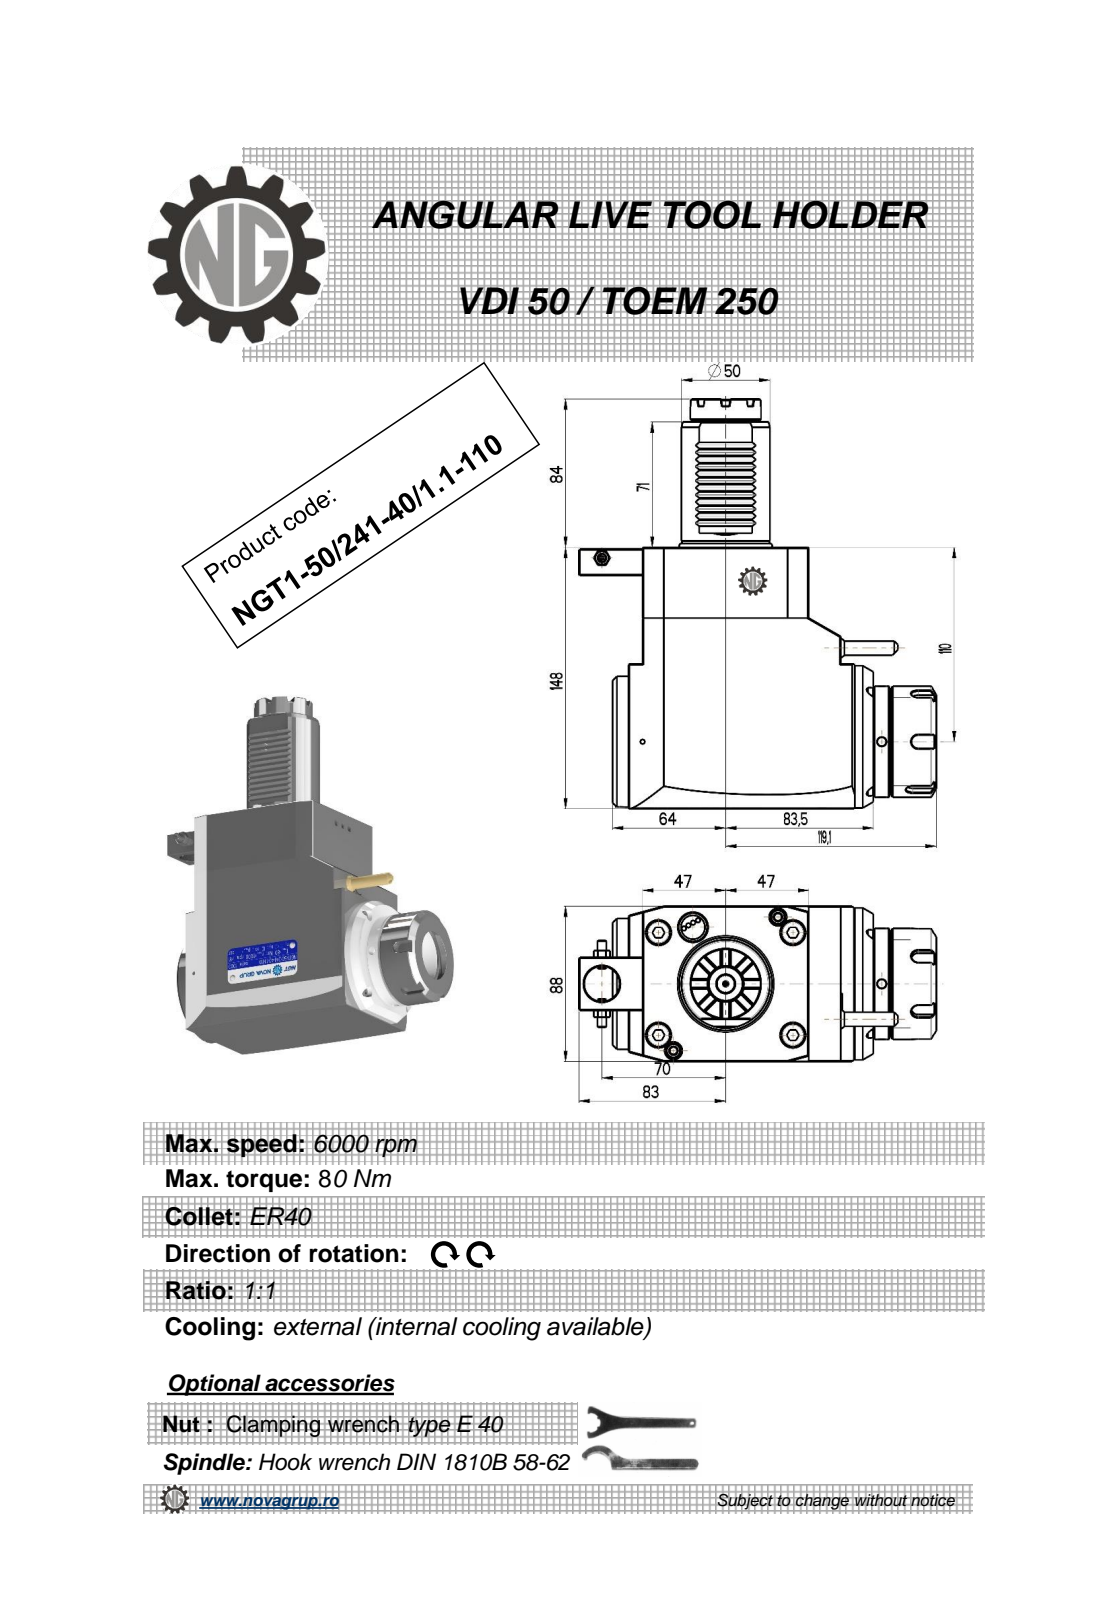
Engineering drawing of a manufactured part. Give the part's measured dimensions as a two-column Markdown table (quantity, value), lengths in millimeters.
| quantity | value |
| --- | --- |
| part name | NGT1_50_241_40_1_1_110 |
| STEP written by | PRO/ENGINEER BY PARAMETRIC TECHNOLOGY CORPORATION, 2010280 (CONFIG_CONTROL_DESIGN) |
| units | millimeters |
| bodies | 1 solid, 473 faces (234 planar, 90 cylindrical, 149 other) |
| overall size | 232 × 202.1 × 88 |
| volume | 1 841 000 mm³ |
| surface area | 116 928 mm² |
| round holes (diameter × count) | 5 × 3, 3 × 1, 9.5 × 1, 20 × 1, 33.5 × 1 |
| round bosses / shafts (diameter × count) | 86 × 1, 74 × 1, 63 × 1, 51 × 1, 50 × 1, 40 × 1, 20.5 × 1, 10 × 1 |
| partial cylindrical surfaces (radius × count) | 0.26 × 12, 0.3 × 12, 0.2 × 6, 3.75 × 5 |
| main face-to-face distances | 88, 148, 147.5, 8, 17, 9, 111, 94, 130.5, 36.5 |
| hole center spacings | 52.46, 56.65, 101.5, 158.25 |
